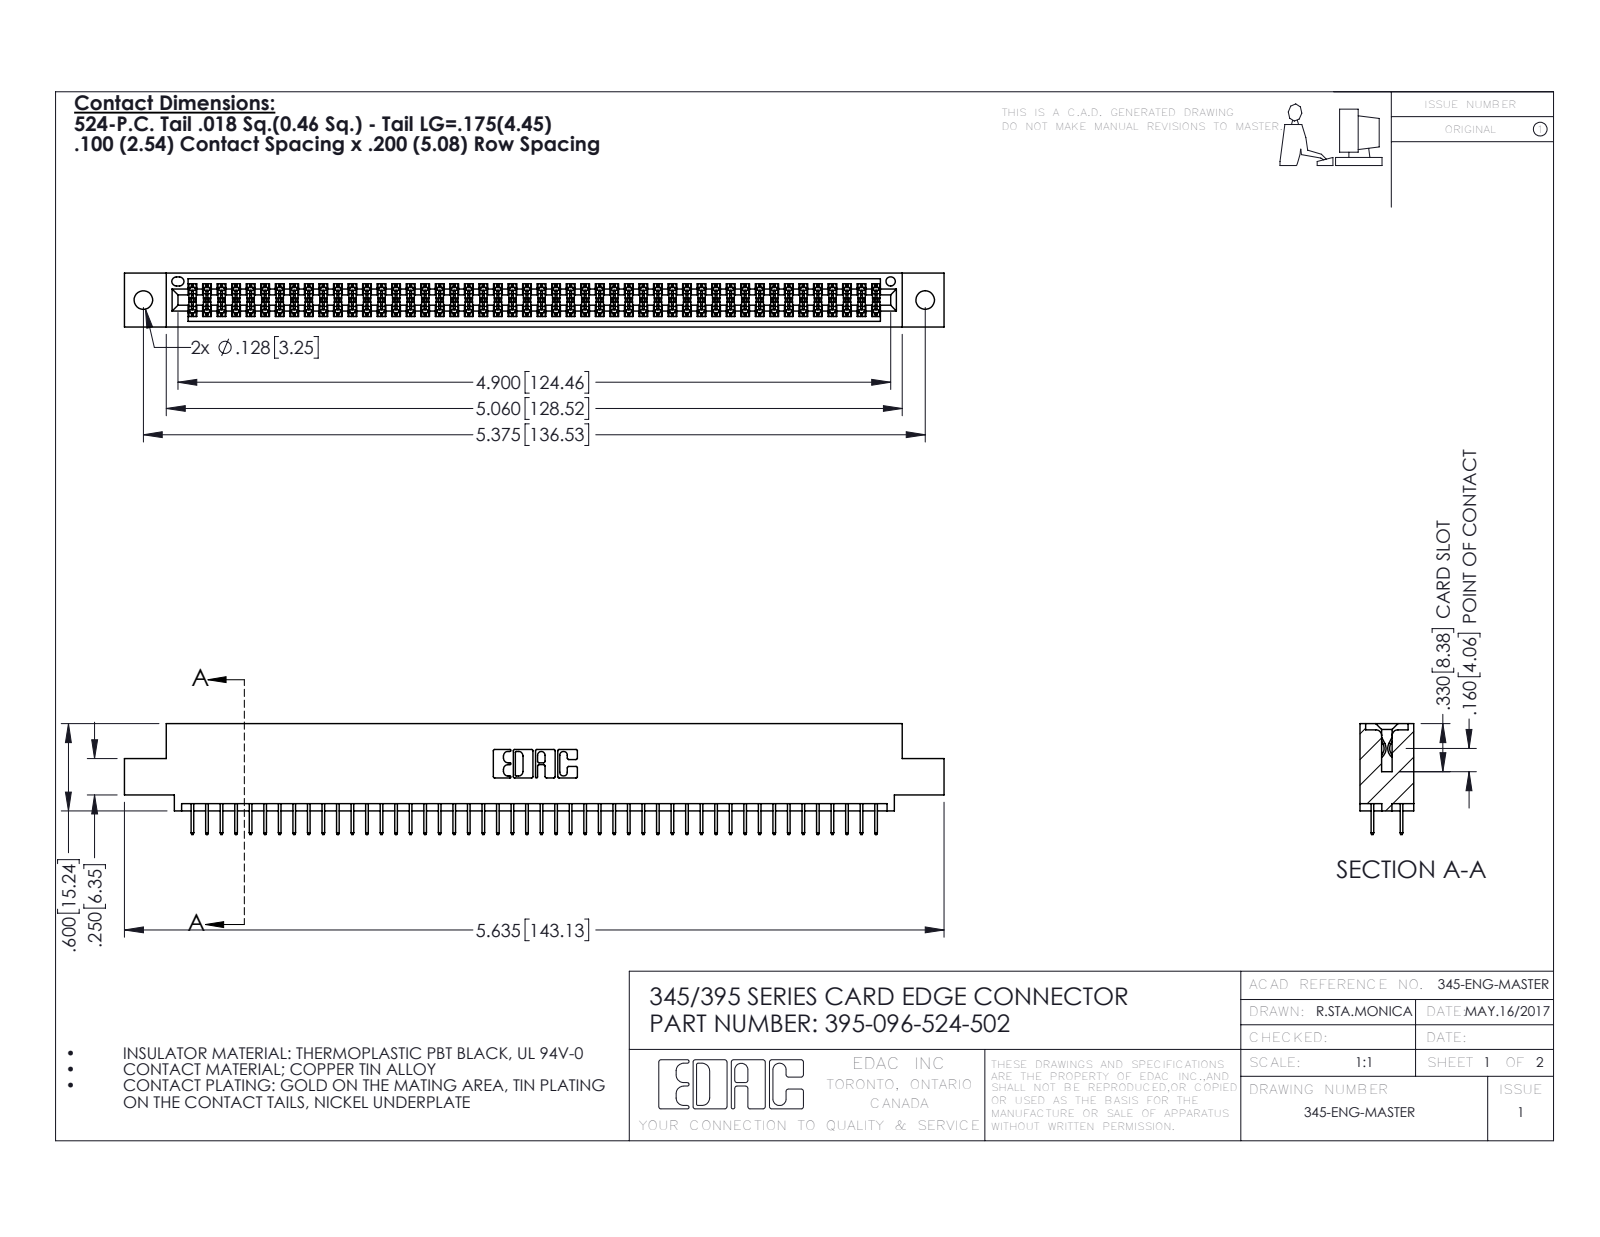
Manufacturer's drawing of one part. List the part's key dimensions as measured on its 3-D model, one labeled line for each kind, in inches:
Part name (STEP PRODUCT): 345-292-001_345-293-124; 395-096-524-502; 345 Part_0.110 Offset - 0.128 Dia
STEP written by: SolidWorks 2016 (CONFIG_CONTROL_DESIGN)
Units: inches
Bodies: 97 solids, 5314 faces (3828 planar, 1486 cylindrical, 0 other)
Overall size (bounding box): 5.635 × 0.762 × 0.37
Volume: 0.836 in³ · Surface area: 30.71 in²
Round holes (diameter × count): ⌀0.128 ×2, ⌀0.064 ×1
Partial cylindrical surfaces — rounded edges, fillets, slot ends (radius × count): R0.006 ×144, R0.01 ×22, R0.007 ×6, R0.031 ×6, R0.026 ×3, R0.014 ×2, R0.019 ×2, R0.022 ×2
Main face-to-face distances: 0.072, 0.298, 0.2, 0.37, 0.098, 0.272, 0.025, 0.225, 0.072, 0.175
Hole centre spacings: 0.27, 5.139, 5.375
